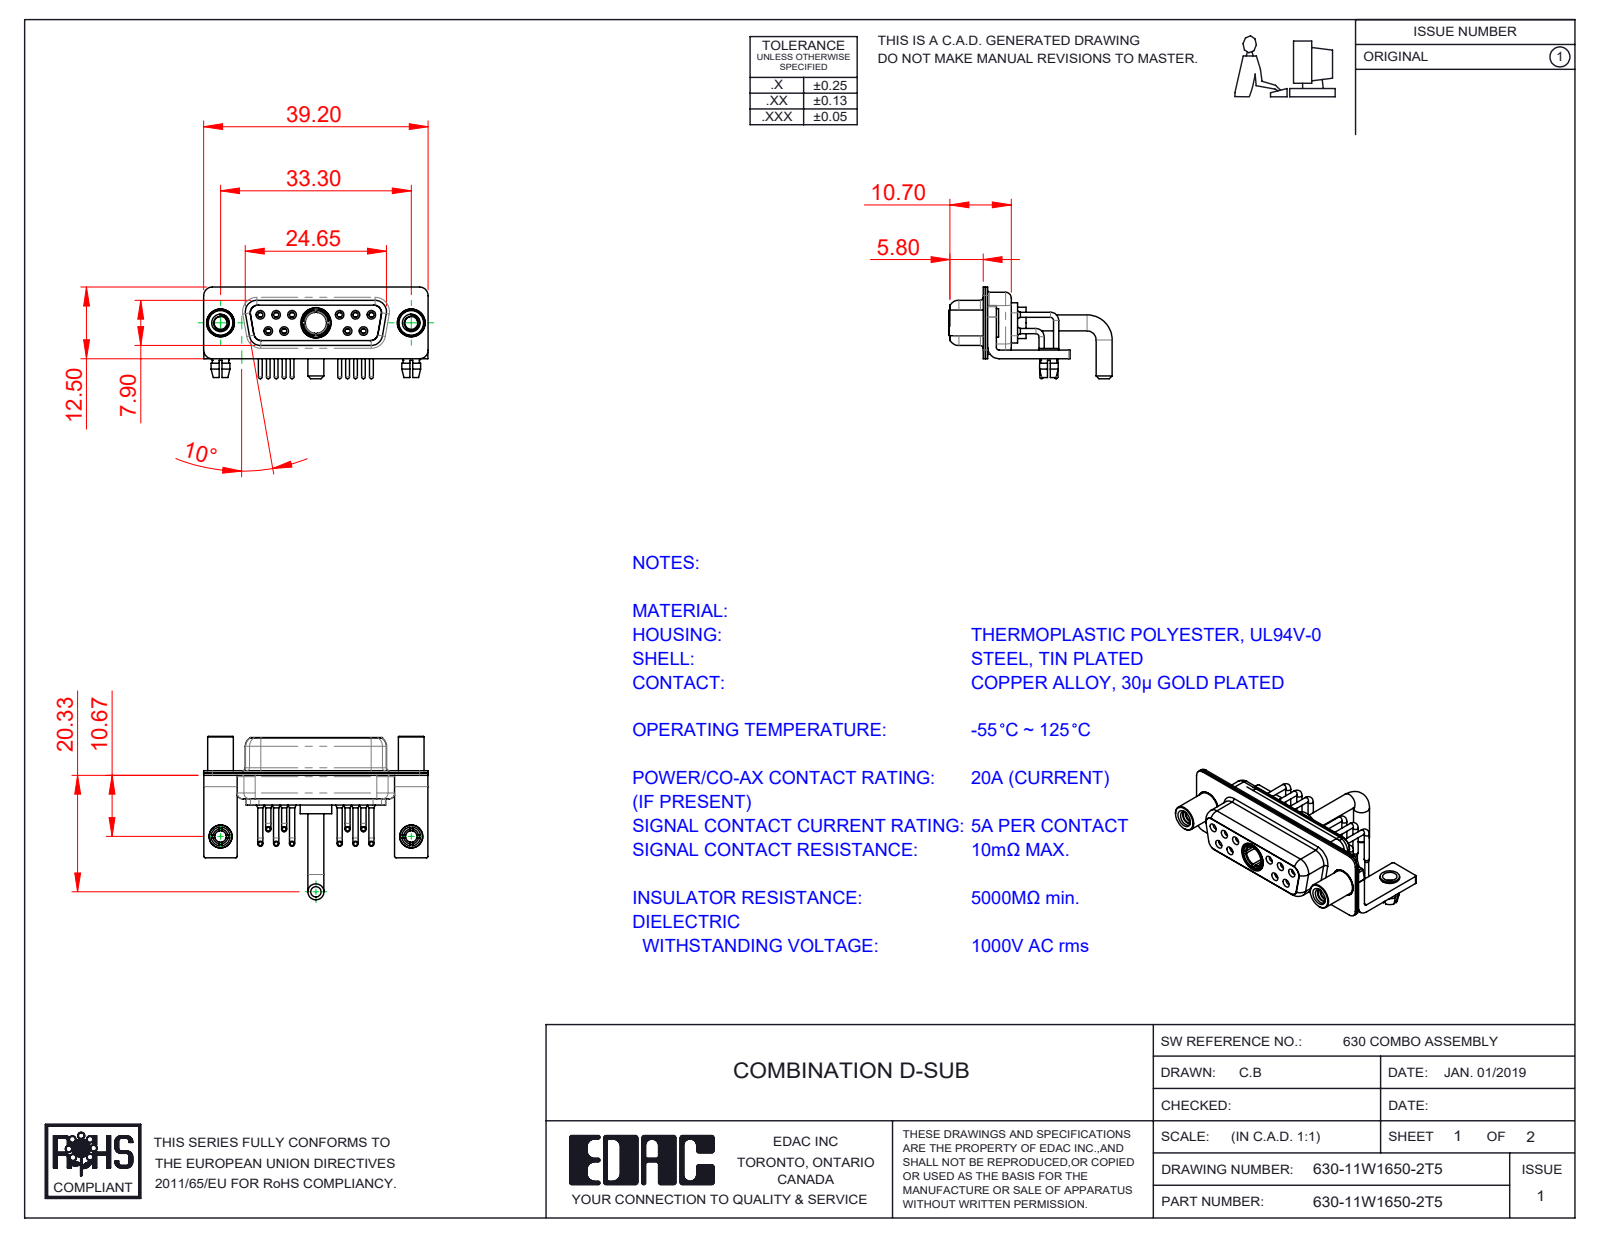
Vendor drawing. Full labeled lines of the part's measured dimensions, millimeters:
Part name (STEP PRODUCT): 630Combo Threaded Standoff_5; 630Combo Shell Front_15 Contacts; 630Combo Board Lock; 630-11W1650-2T5 (+6 more)
STEP written by: SolidWorks 2020 (CONFIG_CONTROL_DESIGN)
Units: millimetres
Bodies: 21 solids, 1067 faces (316 planar, 484 cylindrical, 267 other)
Overall size (bounding box): 39.2 × 28.53 × 16
Volume: 3 123 mm³ · Surface area: 7 460 mm²
Round holes (diameter × count): ⌀2 ×12, ⌀0.9 ×10, ⌀1.1 ×10, ⌀1.5 ×10, ⌀1.7 ×6, ⌀1.6 ×4, ⌀4.85 ×3, ⌀2.26 ×2, ⌀2.5 ×2, ⌀3.2 ×2, ⌀4 ×2, ⌀4.05 ×2
Round bosses / shafts (diameter × count): ⌀0.9 ×10, ⌀0.65 ×10, ⌀1.6 ×6, ⌀5 ×2, ⌀4.95 ×2, ⌀4.8 ×2, ⌀4.5 ×2, ⌀4 ×2
Partial cylindrical surfaces — rounded edges, fillets, slot ends (radius × count): R0.25 ×16, R1.5 ×16, R2 ×13, R1.35 ×12, R1.6 ×8, R0.5 ×5, R0.6 ×4, R0.65 ×4
Main face-to-face distances: 0.4, 0.8, 0.45, 1.4, 8.45, 1.5, 1.8, 8.9, 6.2, 2.3
Hole centre spacings: 3.16, 2.77, 13.85, 11.08, 16.62, 5.03, 5.04, 5.54
